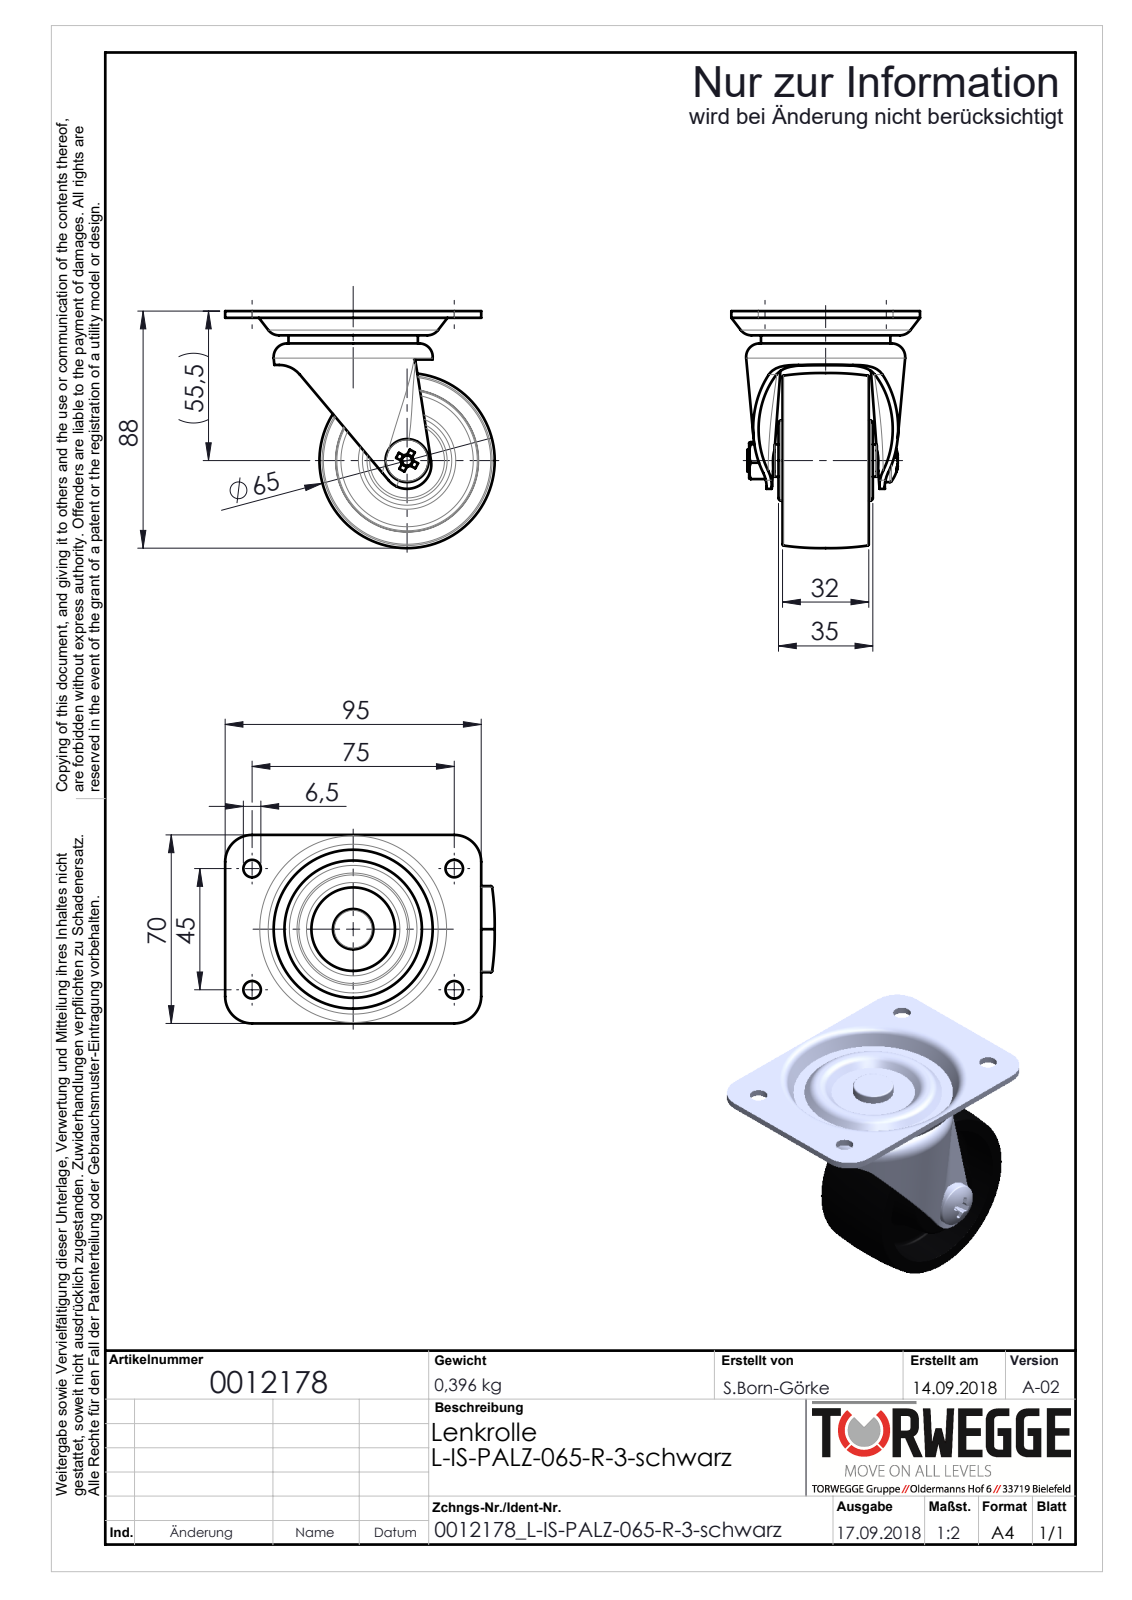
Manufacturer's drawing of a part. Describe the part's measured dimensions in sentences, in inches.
The part is named "0012178_L-IS-PALZ-065-R-3-schwarz". Its 3-D file was written by "SolidWorks 2018 (AUTOMOTIVE_DESIGN)". It is 5 solids with 197 faces: 62 planar, 37 cylindrical and 98 other. Overall it measures 3.938 by 3.465 by 2.756 inches. Its volume is 6.814 cubic inches and its surface area 79.52 square inches. Round holes: 4 of diameter 0.256, 1 of diameter 0.268, 1 of diameter 0.315, 1 of diameter 0.339, 1 of diameter 0.472. Round bosses or shafts: 1 of diameter 1.89, 1 of diameter 0.63, 1 of diameter 0.591. Partial cylindrical surfaces (rounded edges, fillets, slot ends): 5 of radius 0.394, 1 of radius 0.354. The main face-to-face distances are 0.098, 0.551, 0.453, 0.531, 0.728, 0.236, 0.197, 0.315, 0.138, 0.059. The hole center spacings are 1.772, 2.953, 3.443.
